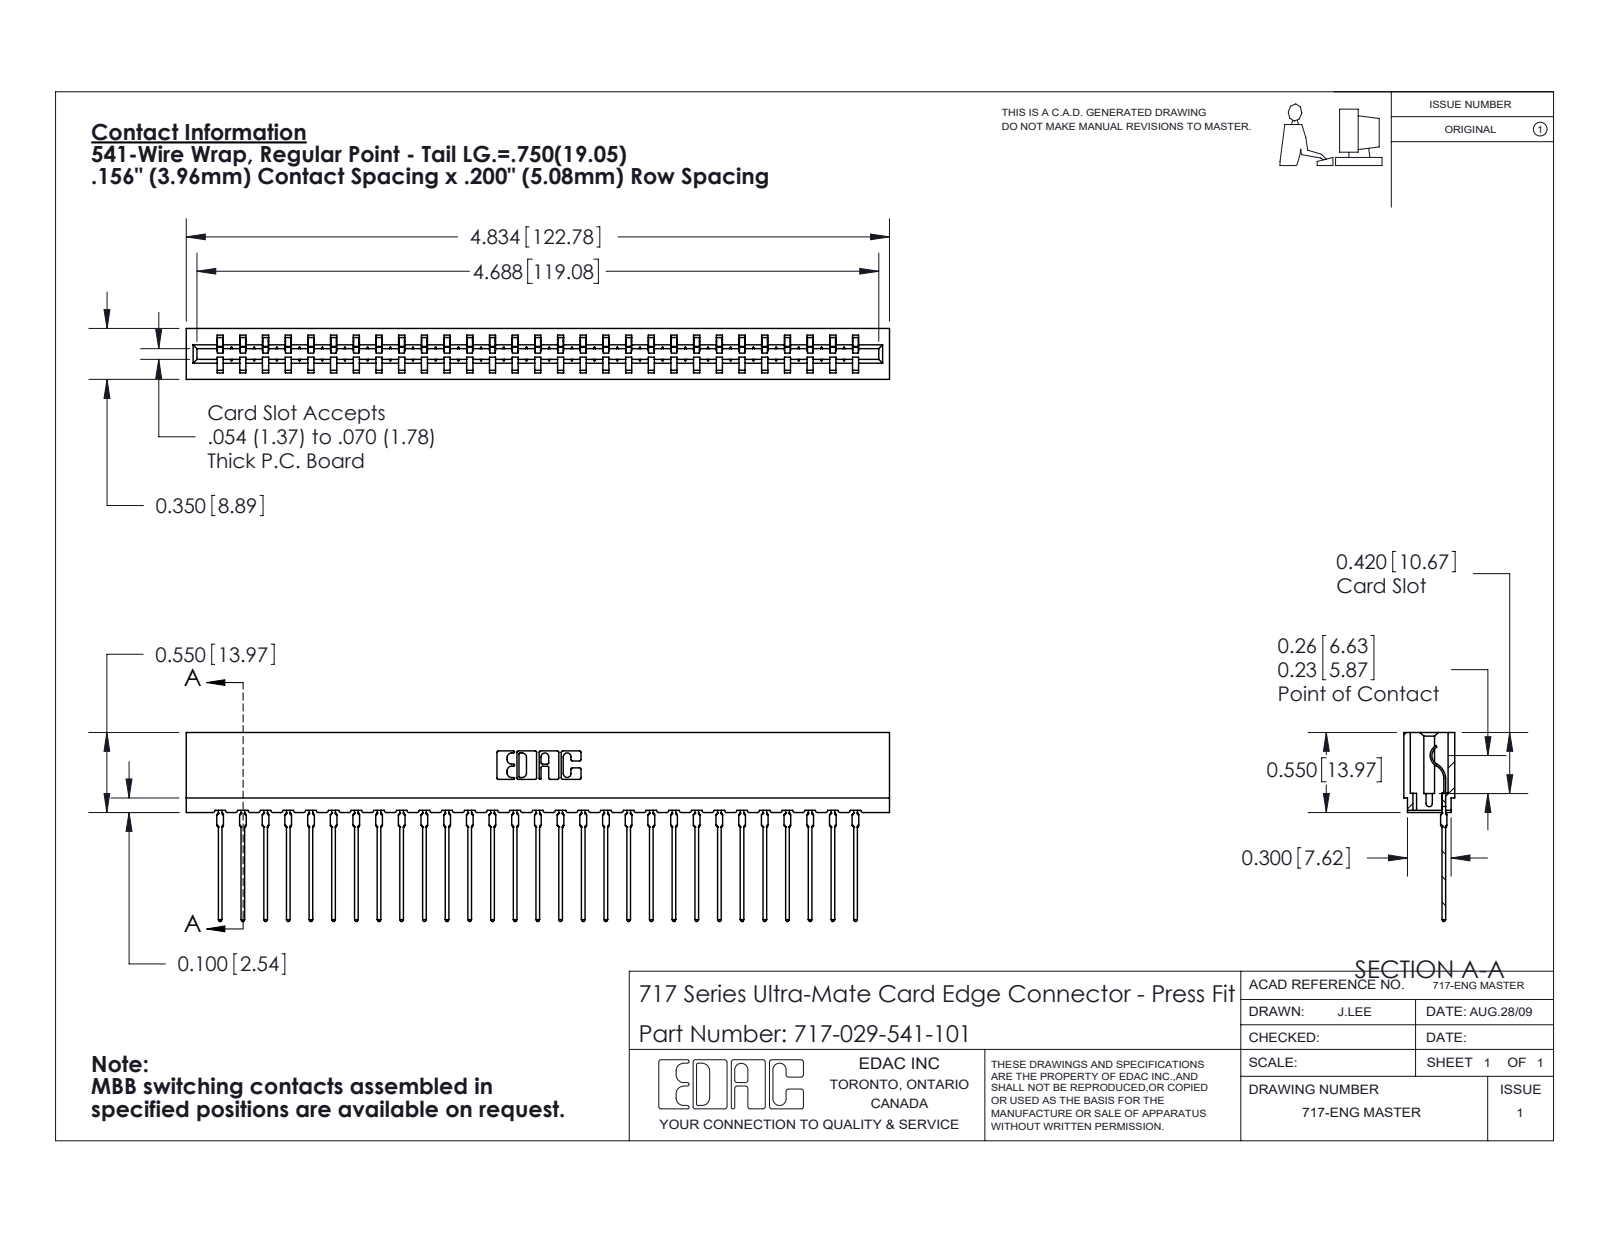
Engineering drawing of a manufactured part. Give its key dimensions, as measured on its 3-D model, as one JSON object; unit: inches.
{"part_name": "745-292-001_541; 717-029-541-101; 717 Part_Insulator Option - 06", "step_written_by": "SolidWorks 2020 (CONFIG_CONTROL_DESIGN)", "units": "inches", "bodies": {"solids": 30, "faces": 3371, "planar": 2026, "cylindrical": 591, "other": 754}, "overall_size": [4.834, 1.299, 0.35], "volume_in3": 0.644, "surface_area_in2": 23.7, "partial_cylinders_radius": [[0.015, 58], [0.021, 58], [0.01, 22], [0.007, 6], [0.031, 6], [0.005, 4], [0.011, 4], [0.026, 3]], "face_to_face_distances": [0.212, 0.138, 0.35, 0.063, 0.287, 0.076, 0.149, 0.074, 0.156, 0.045]}
